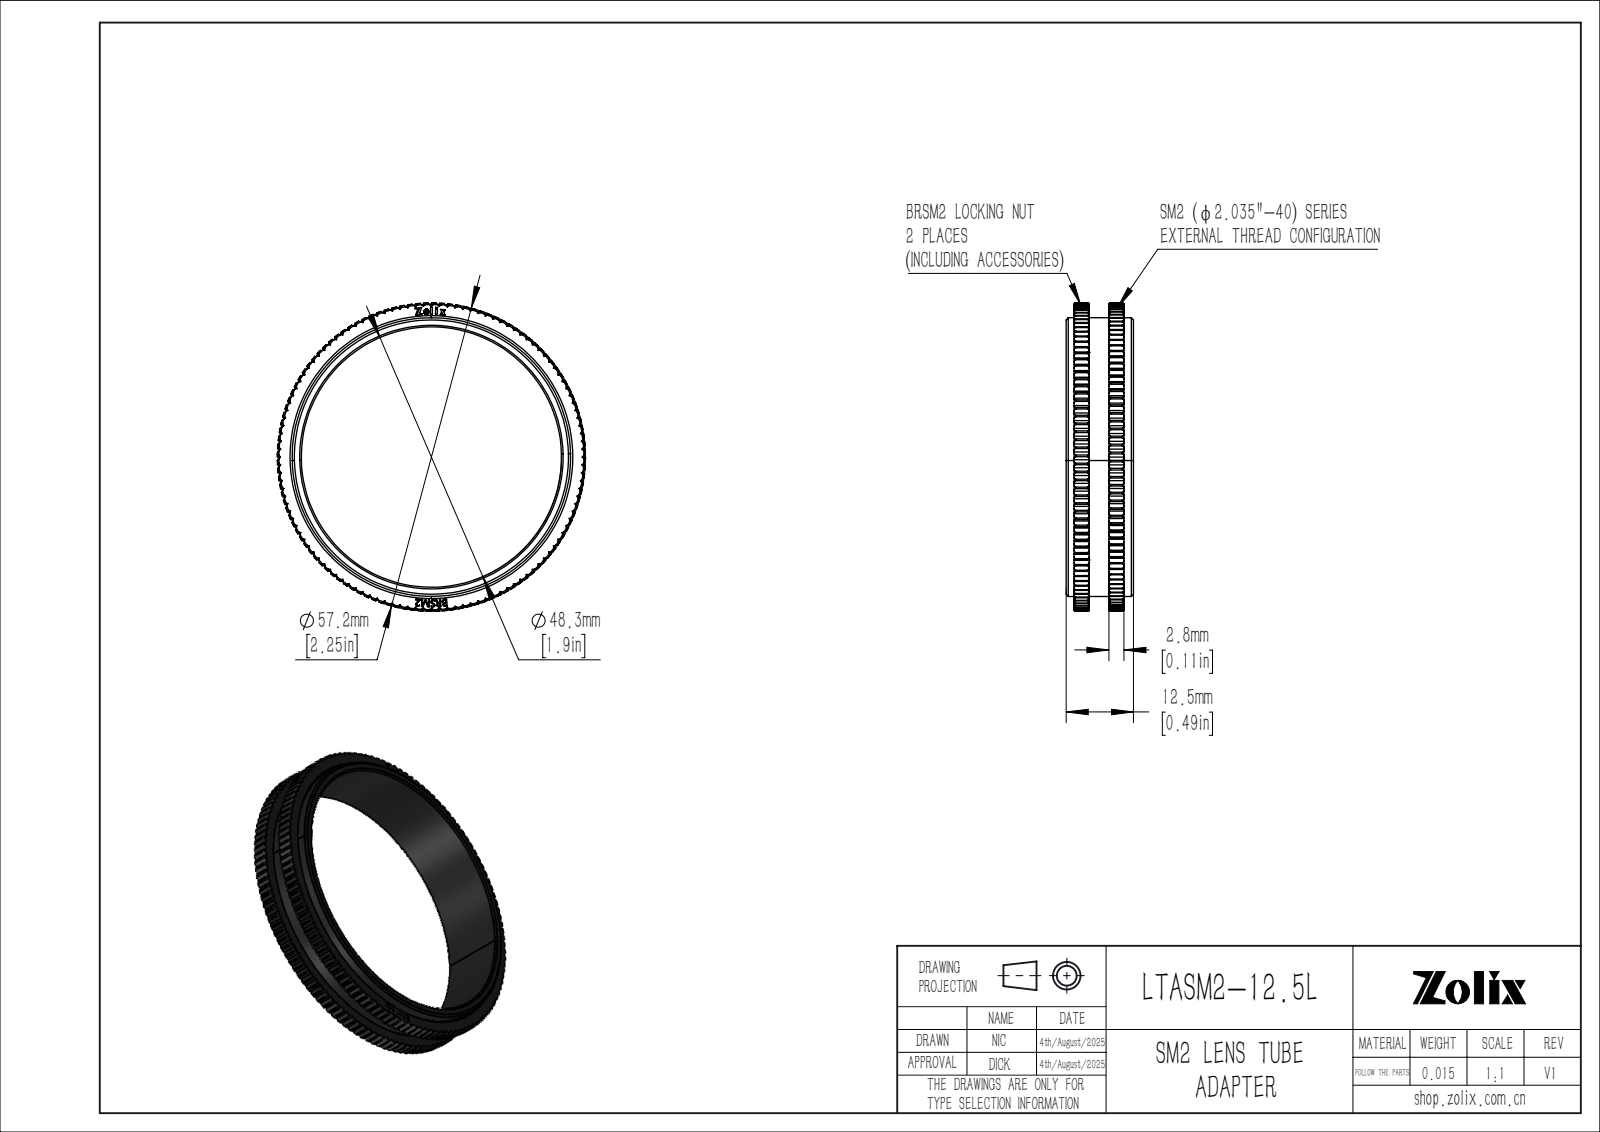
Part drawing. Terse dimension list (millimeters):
name: LTASM2-12.5L
written by: SolidWorks 2020 (CONFIG_CONTROL_DESIGN)
unit: mm
bodies: 3 solids, 1503 faces (702 planar, 248 cylindrical, 553 other)
size: 57.2 × 57.2 × 12.5
volume: 5 633 mm³; area: 8 114 mm²
holes: 1× ⌀48.3, 1× ⌀51.69
rounds: 1× R28.6
face distances: 2.8, 6.46, 3.66, 9.26, 39.59, 39.6, 39.58, 11.03, 10.73, 7.93
